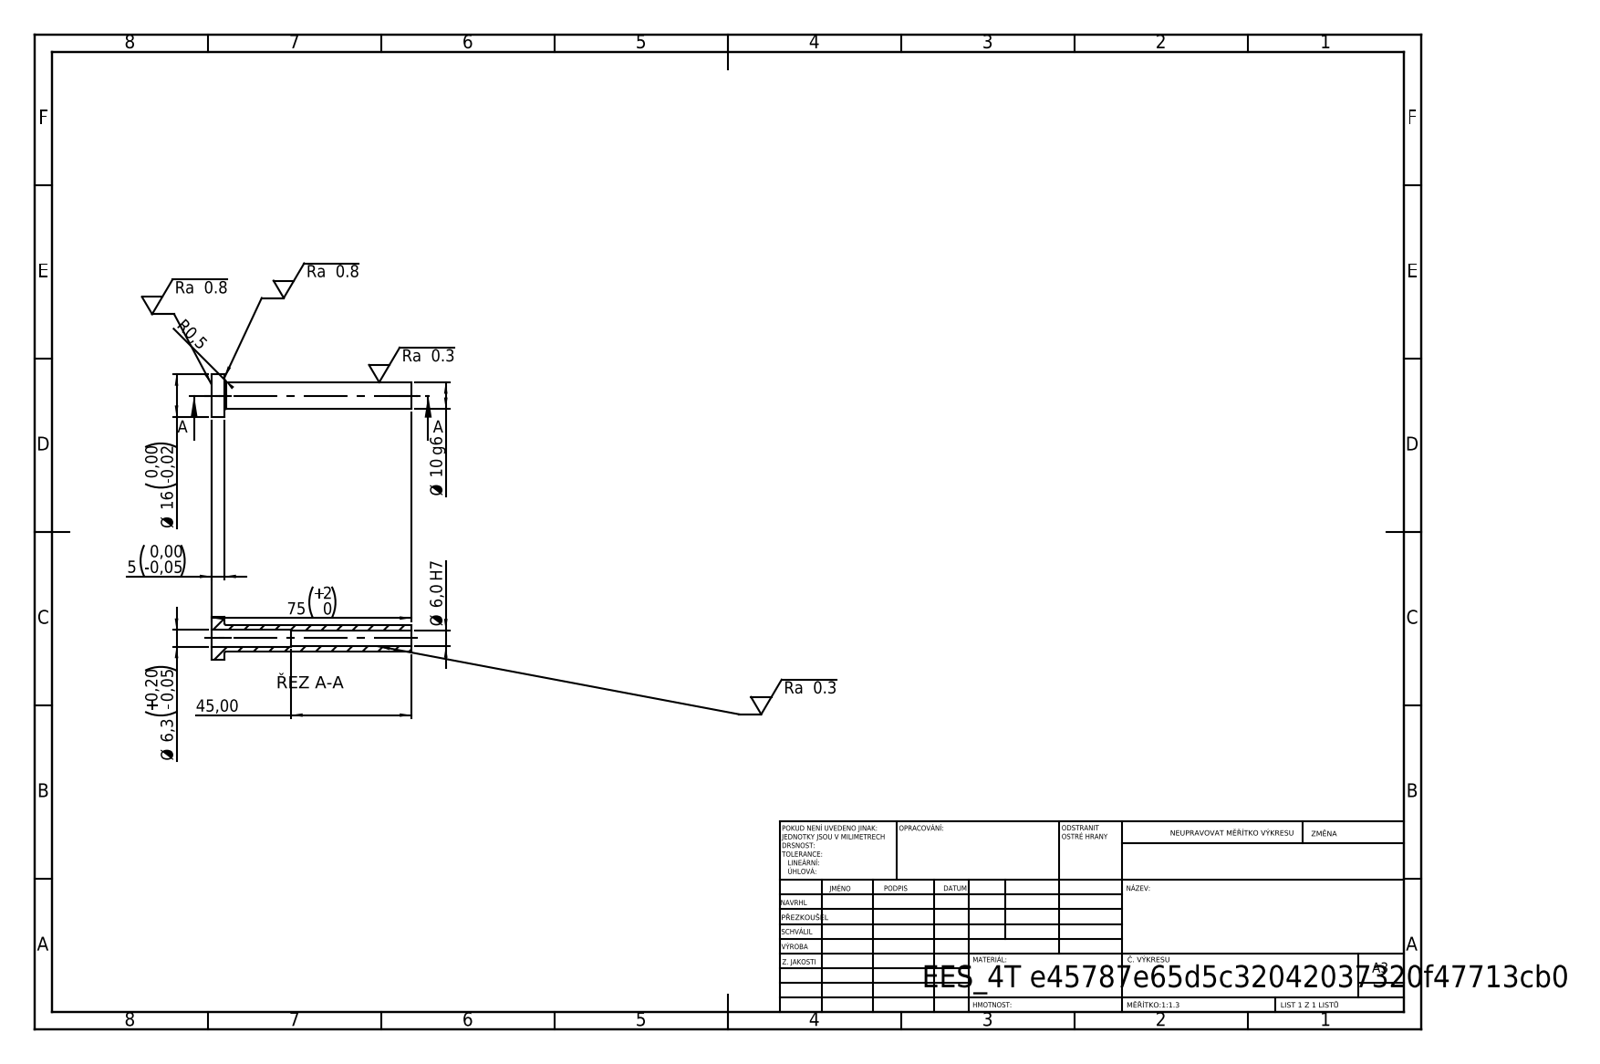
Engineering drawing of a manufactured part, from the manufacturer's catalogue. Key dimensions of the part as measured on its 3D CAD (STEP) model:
STEP written by: SolidWorks 2019 (CONFIG_CONTROL_DESIGN)
Units: millimetres
Bodies: 1 solid, 14 faces (4 planar, 8 cylindrical, 2 other)
Overall size (bounding box): 75 × 16 × 16
Volume: 4 297 mm³ · Surface area: 4 231 mm²
Round holes (diameter × count): ⌀6 ×1, ⌀6.3 ×1
Round bosses / shafts (diameter × count): ⌀16 ×1, ⌀10 ×1
Main face-to-face distances: 5, 75, 70, 30, 25, 45
